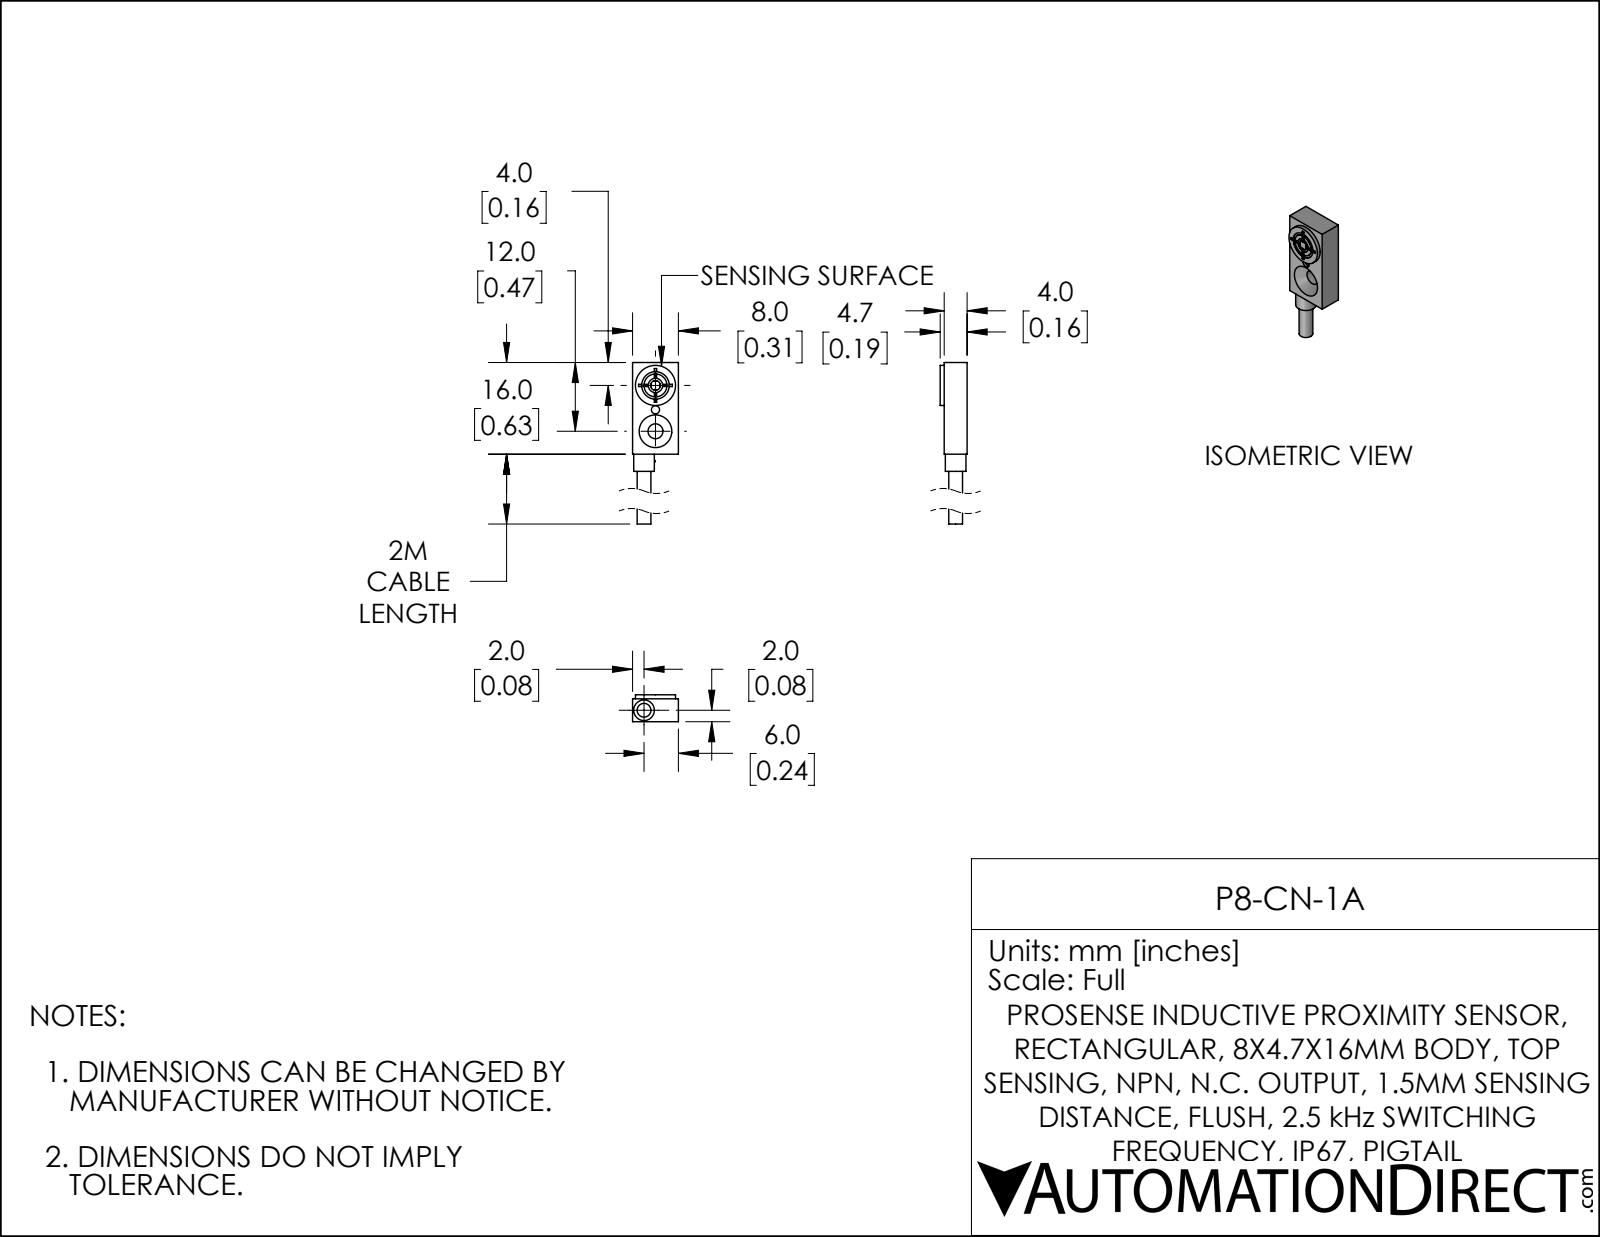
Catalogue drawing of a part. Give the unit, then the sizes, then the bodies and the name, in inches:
Units: inches
Overall size (bounding box): 0.992 × 0.315 × 0.185
Round holes (diameter × count): ⌀0.056 ×1, ⌀0.098 ×1, ⌀0.102 ×1, ⌀0.189 ×1
Round bosses / shafts (diameter × count): ⌀0.276 ×1, ⌀0.157 ×1, ⌀0.142 ×1, ⌀0.094 ×1
Partial cylindrical surfaces — rounded edges, fillets, slot ends (radius × count): R0.033 ×1
Main face-to-face distances: 0.315, 0.157, 0.185, 0.028, 0.63, 0.183, 0.026, 0.748, 0.118, 0.992
Hole centre spacings: 0.148, 0.167, 0.315
Volume: 0.034 in³ · Surface area: 0.878 in²
Bodies: 1 solid, 70 faces (48 planar, 21 cylindrical, 1 other)
Part name (STEP PRODUCT): P8-CN-1A
STEP written by: SolidWorks 2019 (CONFIG_CONTROL_DESIGN)
